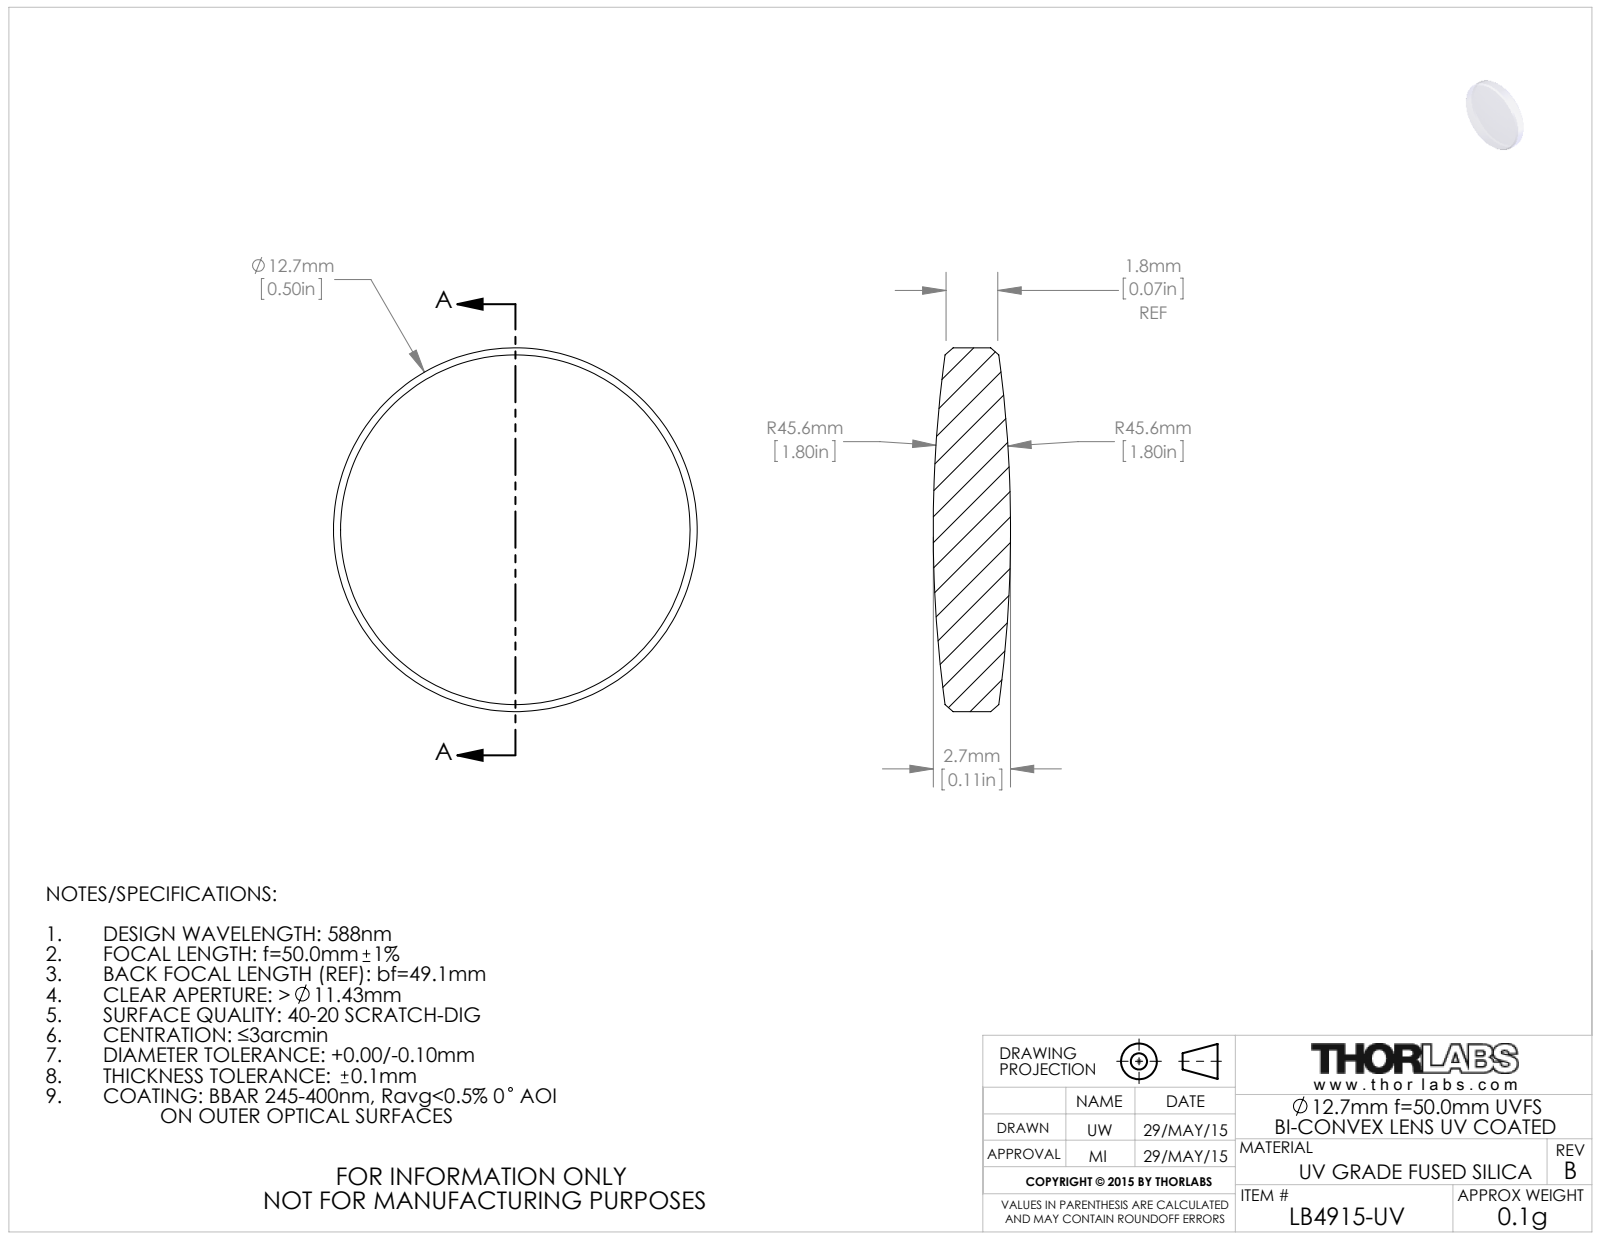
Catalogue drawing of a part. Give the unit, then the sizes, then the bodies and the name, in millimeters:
Units: millimetres
Overall size (bounding box): 12.7 × 12.7 × 2.7
Round bosses / shafts (diameter × count): ⌀12.7 ×1
Volume: 283 mm³ · Surface area: 317 mm²
Bodies: 1 solid, 10 faces (0 planar, 2 cylindrical, 8 other)
Part name (STEP PRODUCT): 4314-E0W
STEP written by: SolidWorks 2014 (CONFIG_CONTROL_DESIGN)
